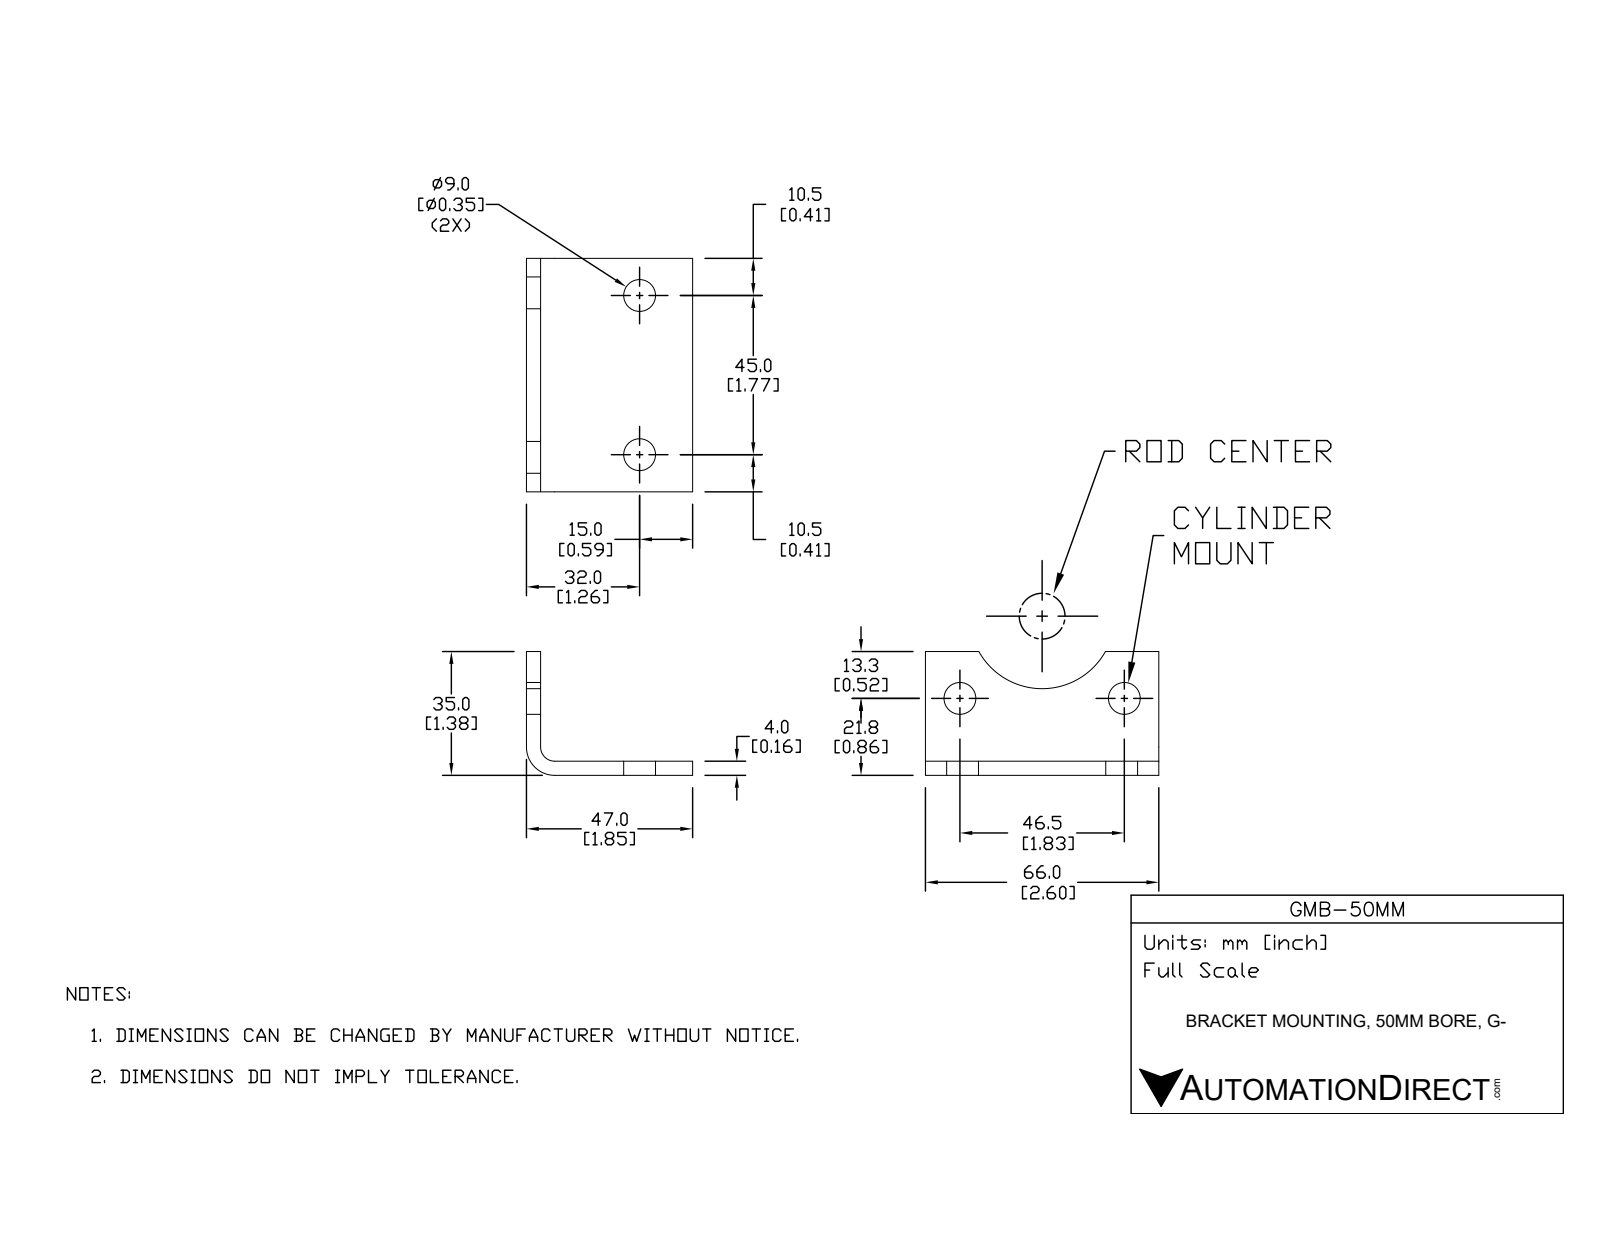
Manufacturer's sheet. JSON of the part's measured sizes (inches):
{"part_name": "GMB-50MM", "step_written_by": "SolidWorks 2017 (AUTOMOTIVE_DESIGN)", "units": "inches", "bodies": {"solids": 1, "faces": 24, "planar": 13, "cylindrical": 11, "other": 0}, "overall_size": [2.598, 1.85, 1.378], "volume_in3": 1.109, "surface_area_in2": 16.6, "round_holes": [[0.354, 4]], "partial_cylinders_radius": [[0.039, 1], [0.197, 1], [0.807, 1]], "face_to_face_distances": [0.157, 2.598, 1.85, 1.693, 1.378, 1.22], "hole_center_spacings": [1.772, 1.831]}
